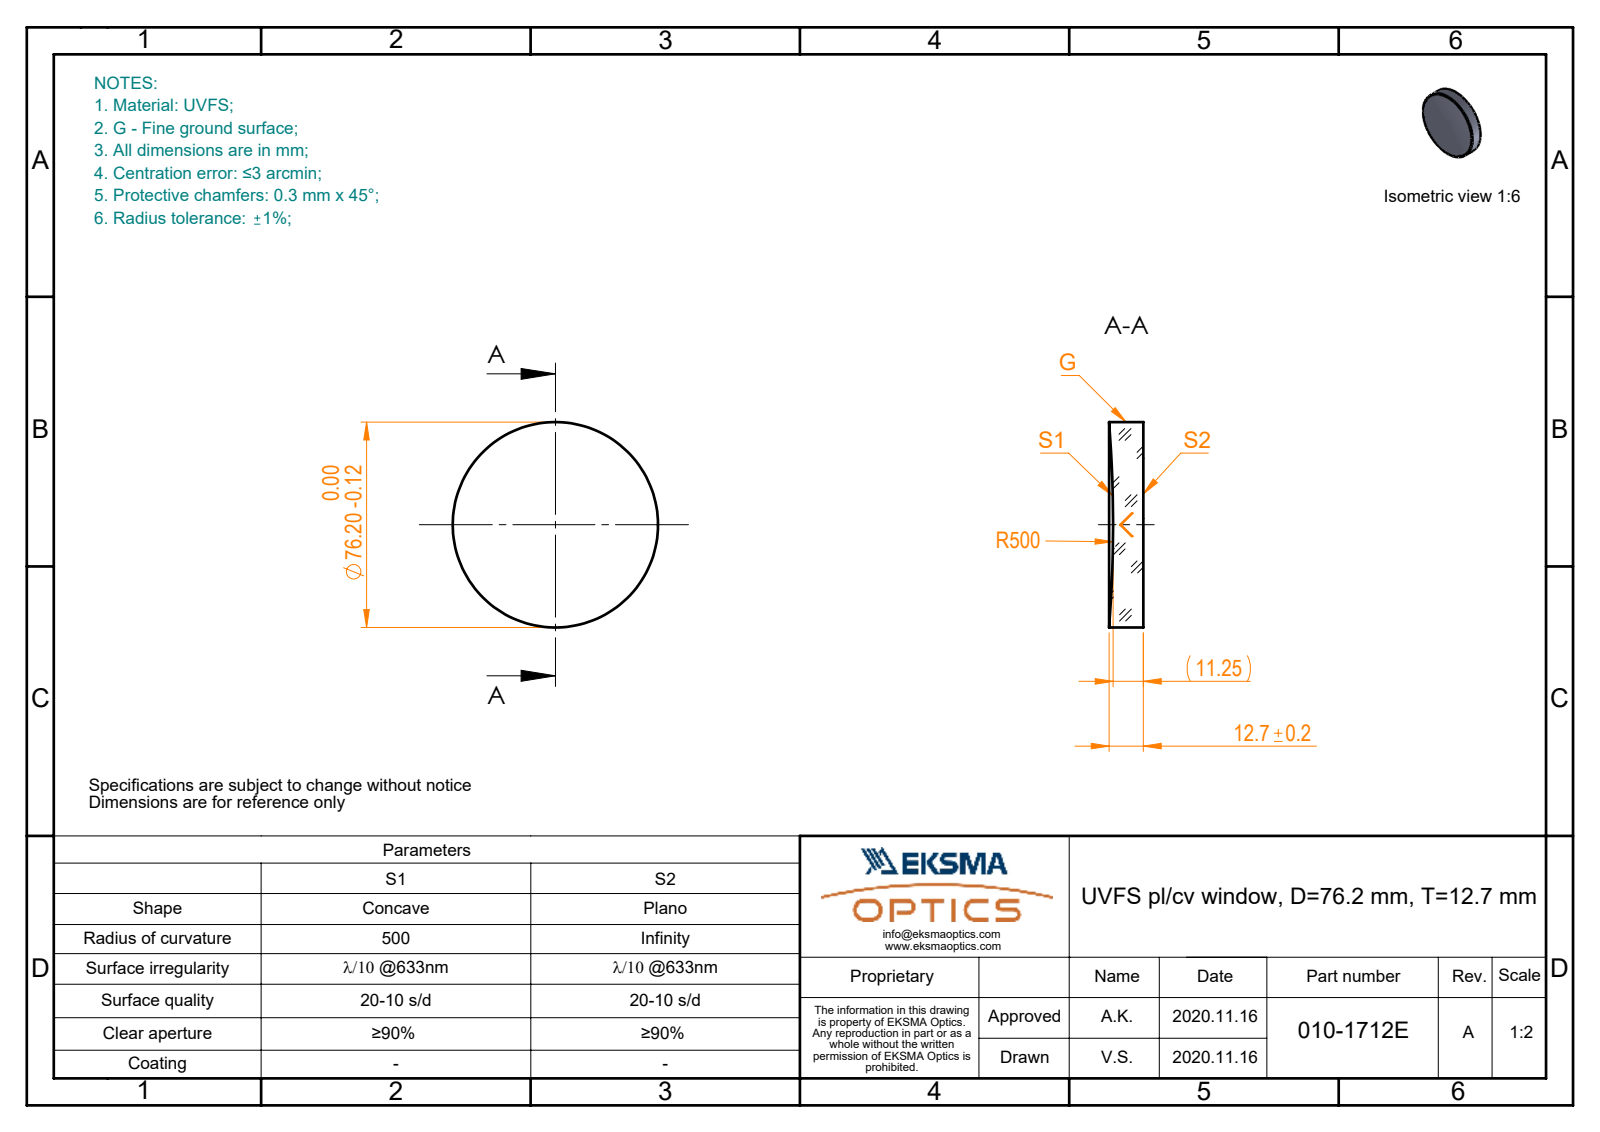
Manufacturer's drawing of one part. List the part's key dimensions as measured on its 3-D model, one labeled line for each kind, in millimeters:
Part name (STEP PRODUCT): 010-1712E_UVFS_PCV_window
STEP written by: SolidWorks 2019 (CONFIG_CONTROL_DESIGN)
Units: millimetres
Bodies: 1 solid, 5 faces (1 planar, 2 cylindrical, 2 other)
Overall size (bounding box): 76.2 × 76.2 × 12.7
Volume: 54 600 mm³ · Surface area: 12 168 mm²
Round bosses / shafts (diameter × count): ⌀76.2 ×1
